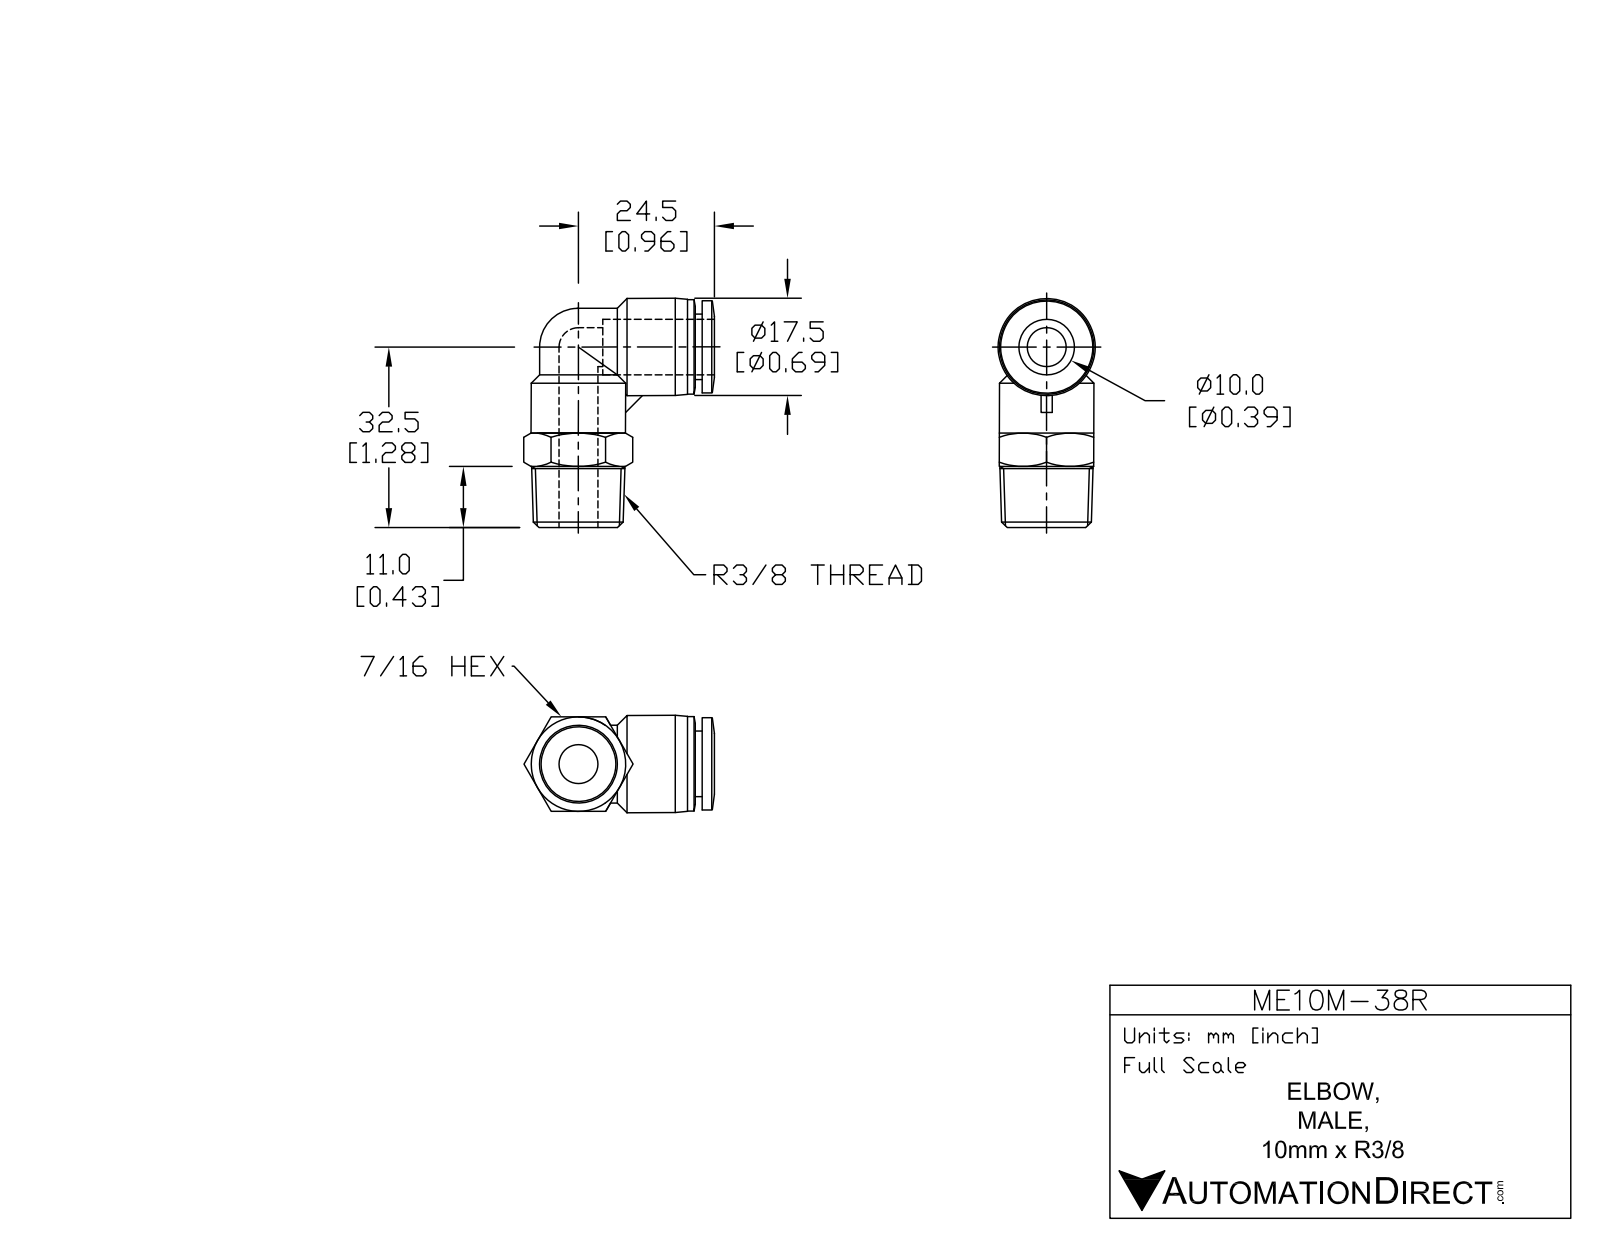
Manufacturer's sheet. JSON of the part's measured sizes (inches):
{"part_name": "ME10M-38R", "step_written_by": "SolidWorks 2015 (AUTOMOTIVE_DESIGN)", "units": "inches", "bodies": {"solids": 1, "faces": 71, "planar": 16, "cylindrical": 20, "other": 35}, "overall_size": [1.624, 1.355, 0.689], "volume_in3": 0.502, "surface_area_in2": 7.756, "round_holes": [[0.315, 2], [0.406, 1]], "round_bosses_or_shafts": [[0.669, 2], [0.689, 1], [0.654, 1], [0.551, 1], [0.465, 1]], "partial_cylinders_radius": [[0.276, 1]], "face_to_face_distances": [0.669, 0.049, 0.659, 0.709, 0.295, 0.374, 0.433, 0.079, 0.604, 0.055]}
